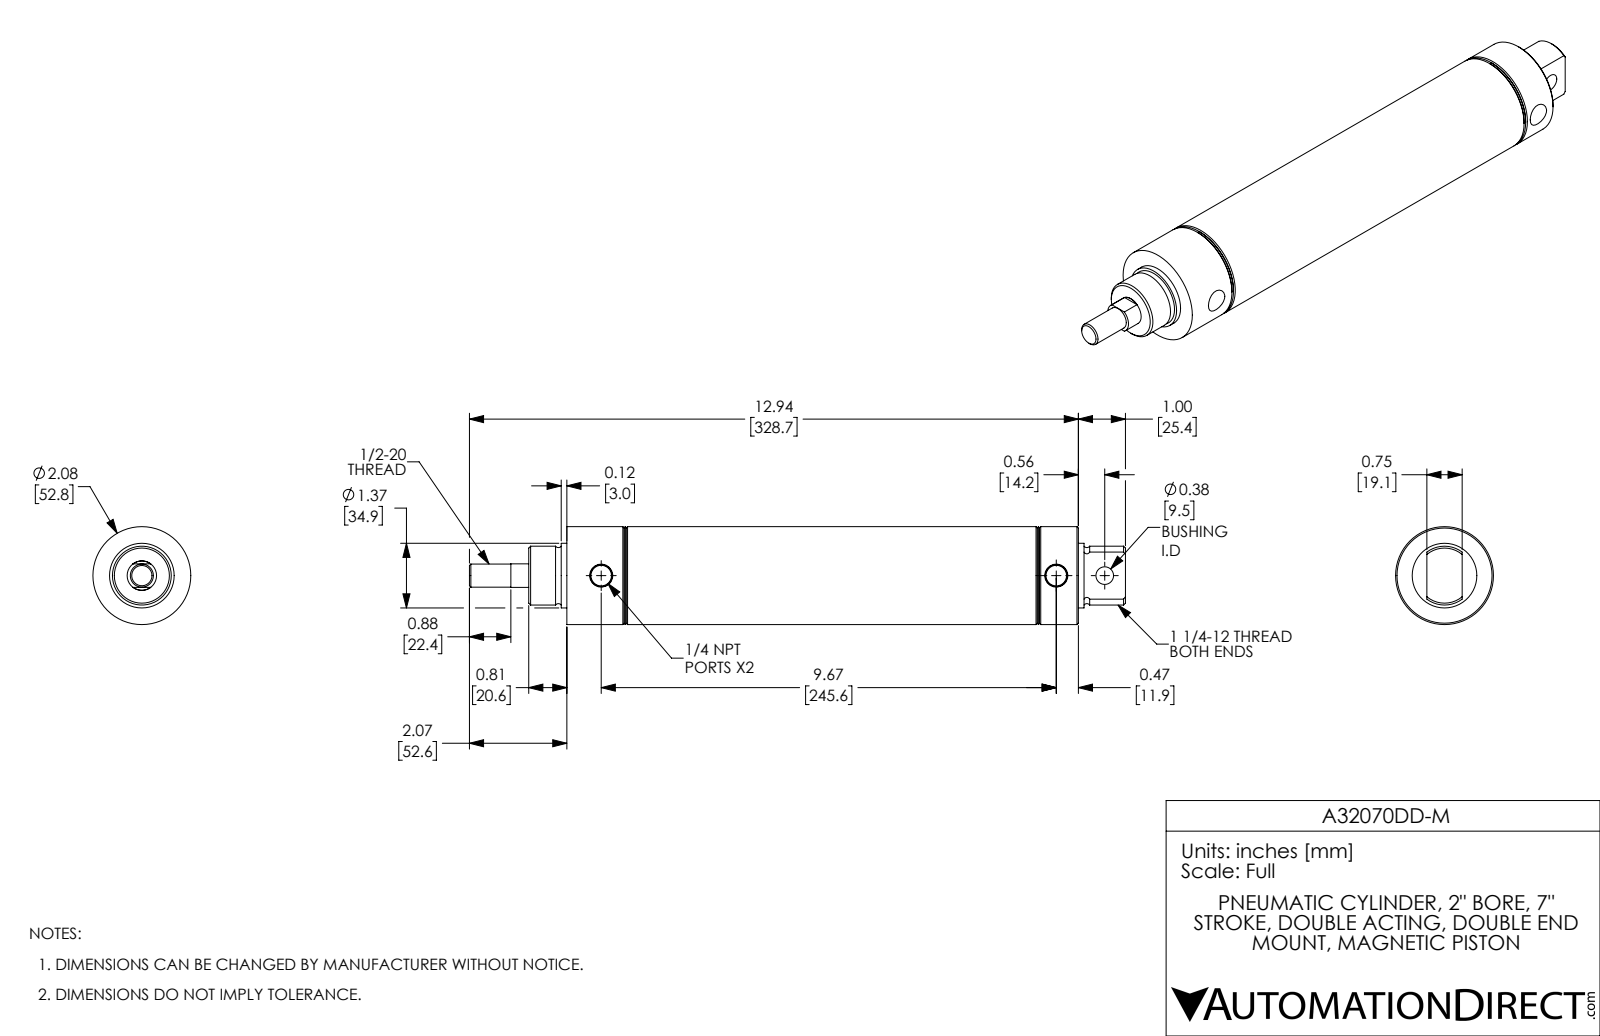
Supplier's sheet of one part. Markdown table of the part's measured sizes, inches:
| quantity | value |
| --- | --- |
| part name | A32070DD-M; A32070DD-M-Rod; A32070DD-M-MainBody |
| STEP written by | SolidWorks 2017 (AUTOMOTIVE_DESIGN) |
| units | inches |
| bodies | 2 solids, 88 faces (20 planar, 30 cylindrical, 38 other) |
| overall size | 13.94 × 2.08 × 2.08 |
| volume | 18.92 in³ |
| surface area | 175.7 in² |
| round holes (diameter × count) | 0.438 × 2, 0.375 × 1, 0.625 × 1, 2 × 1 |
| round bosses / shafts (diameter × count) | 2.08 × 1, 1.373 × 1, 1.25 × 1, 0.491 × 1 |
| main face-to-face distances | 1.685, 9.185, 0.5, 0.5, 7.5, 7.5, 7, 9.185, 8.685, 1.685 |
| hole center spacings | 1.03, 9.67, 10.7 |
